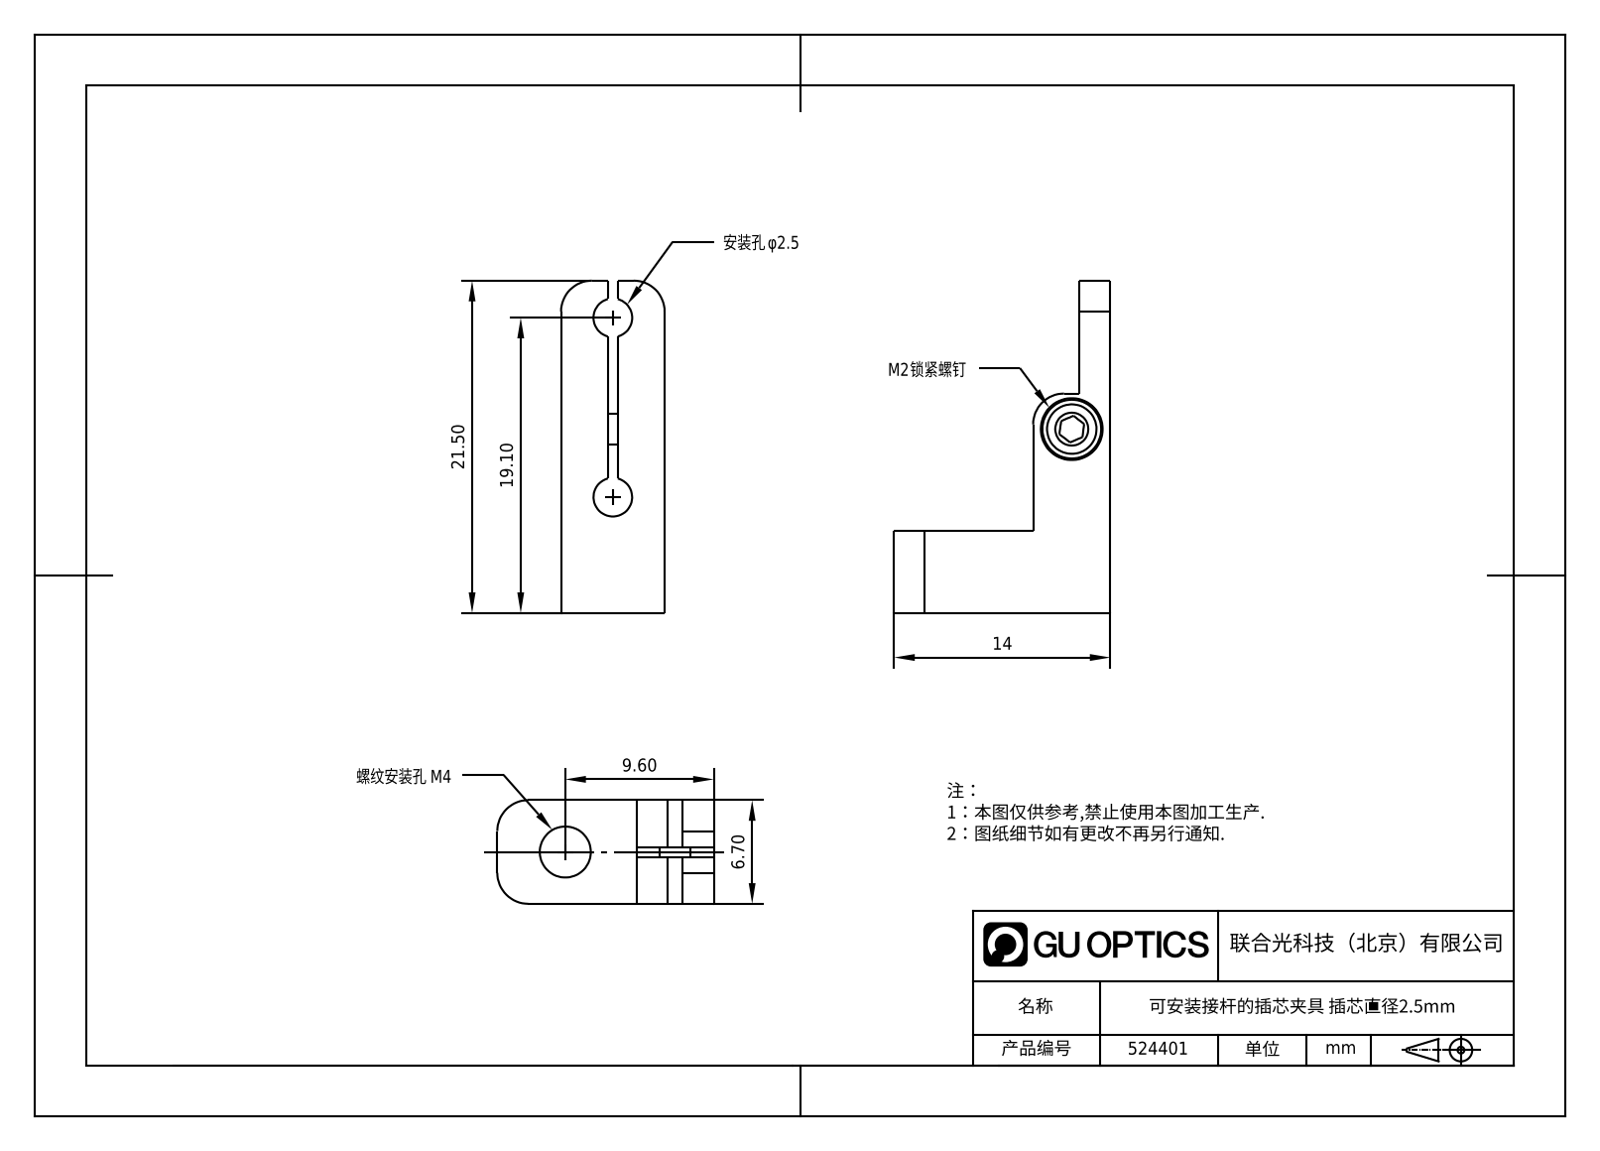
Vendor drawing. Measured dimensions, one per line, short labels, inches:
name: 1.8.3.8-ZFJ-CM25; 30.1.圆柱头内六角不锈钢螺丝_30.1.16-M2*4; 可安装接杆的插芯夹具主体，M4螺孔_1.8.3.8.1-ZFJ-CM25
written by: SolidWorks 2021 (CONFIG_CONTROL_DESIGN)
unit: in
bodies: 2 solids, 60 faces (28 planar, 24 cylindrical, 8 other)
size: 0.846 × 0.551 × 0.264
volume: 0.047 in³; area: 1.47 in²
holes: 2× ⌀0.098, 1× ⌀0.063, 1× ⌀0.094, 1× ⌀0.13, 1× ⌀0.157
bosses: 1× ⌀0.15, 1× ⌀0.079
rounds: 5× R0.079
face distances: 0.264, 0.119, 0.144, 0.209, 0.079, 0.197, 0.118, 0.025, 0.354, 0.472
hole spacings: 0.457
